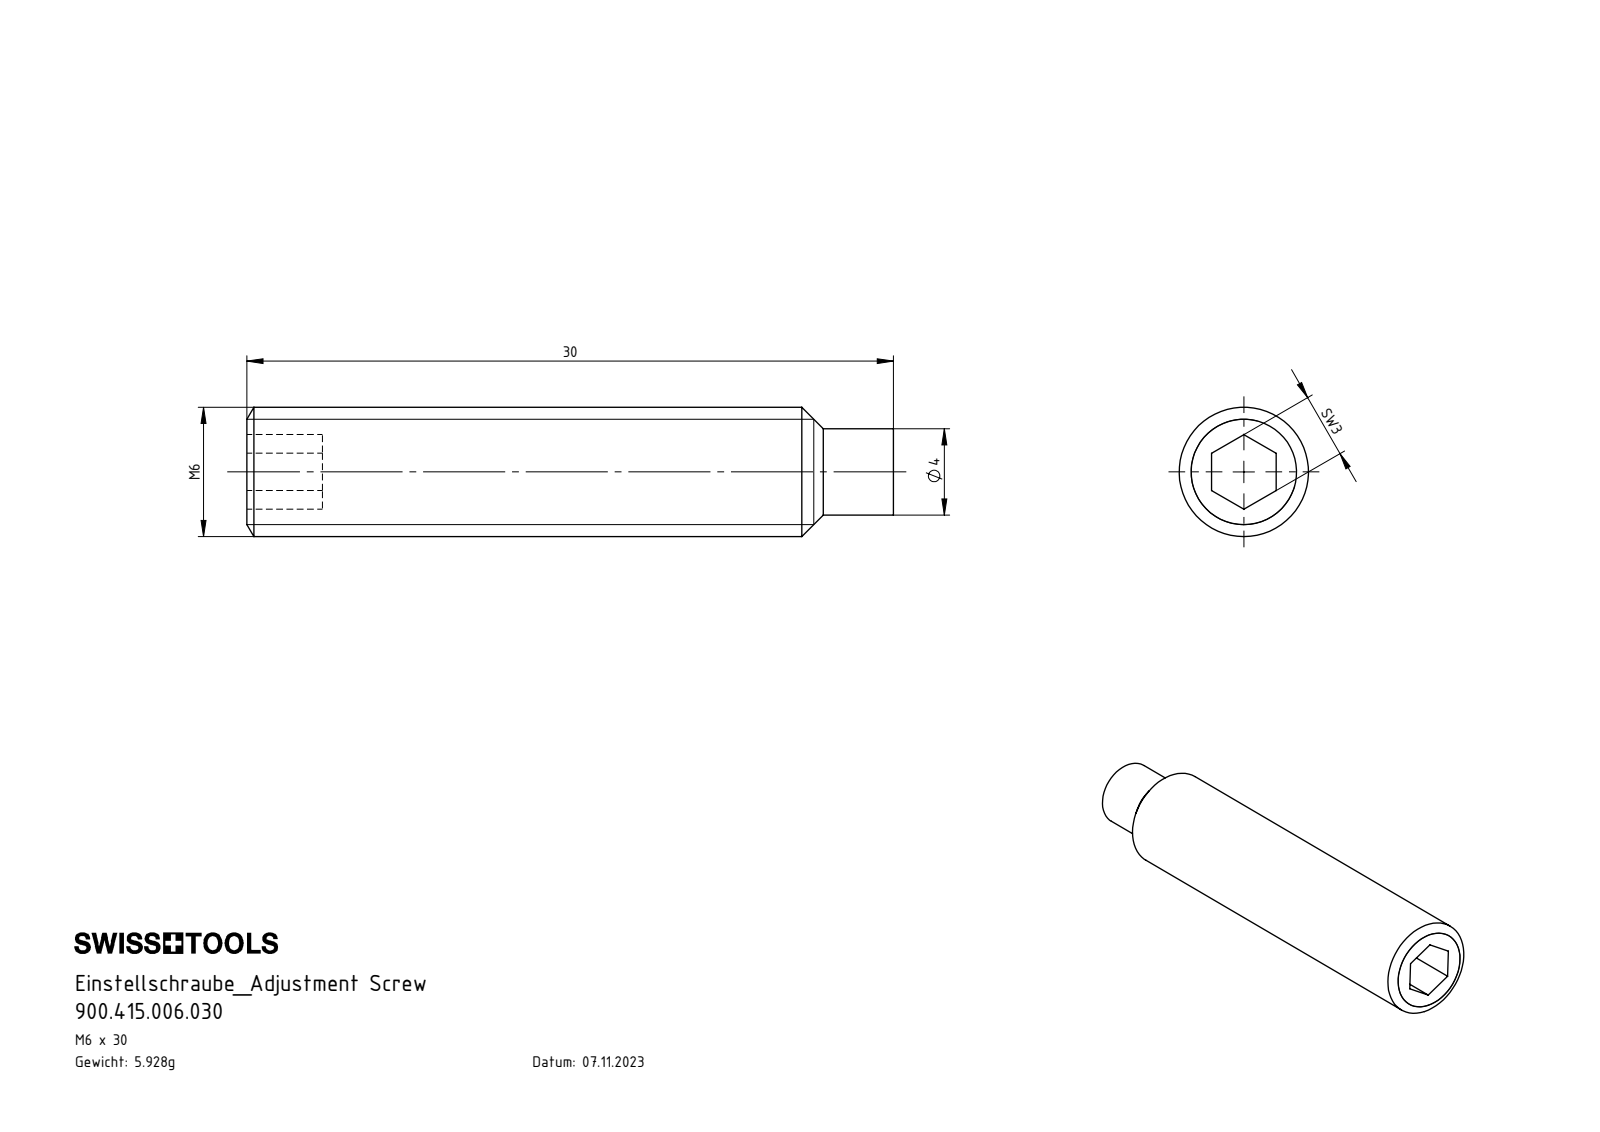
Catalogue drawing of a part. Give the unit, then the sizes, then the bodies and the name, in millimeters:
Units: millimetres
Overall size (bounding box): 30 × 6 × 6
Round bosses / shafts (diameter × count): ⌀6 ×1, ⌀4 ×1
Main face-to-face distances: 3, 30, 3.5, 26.5
Volume: 760 mm³ · Surface area: 621 mm²
Bodies: 1 solid, 17 faces (9 planar, 4 cylindrical, 4 other)
Part name (STEP PRODUCT): 900.415.006.030
STEP written by: SolidWorks 2022 (AUTOMOTIVE_DESIGN)
